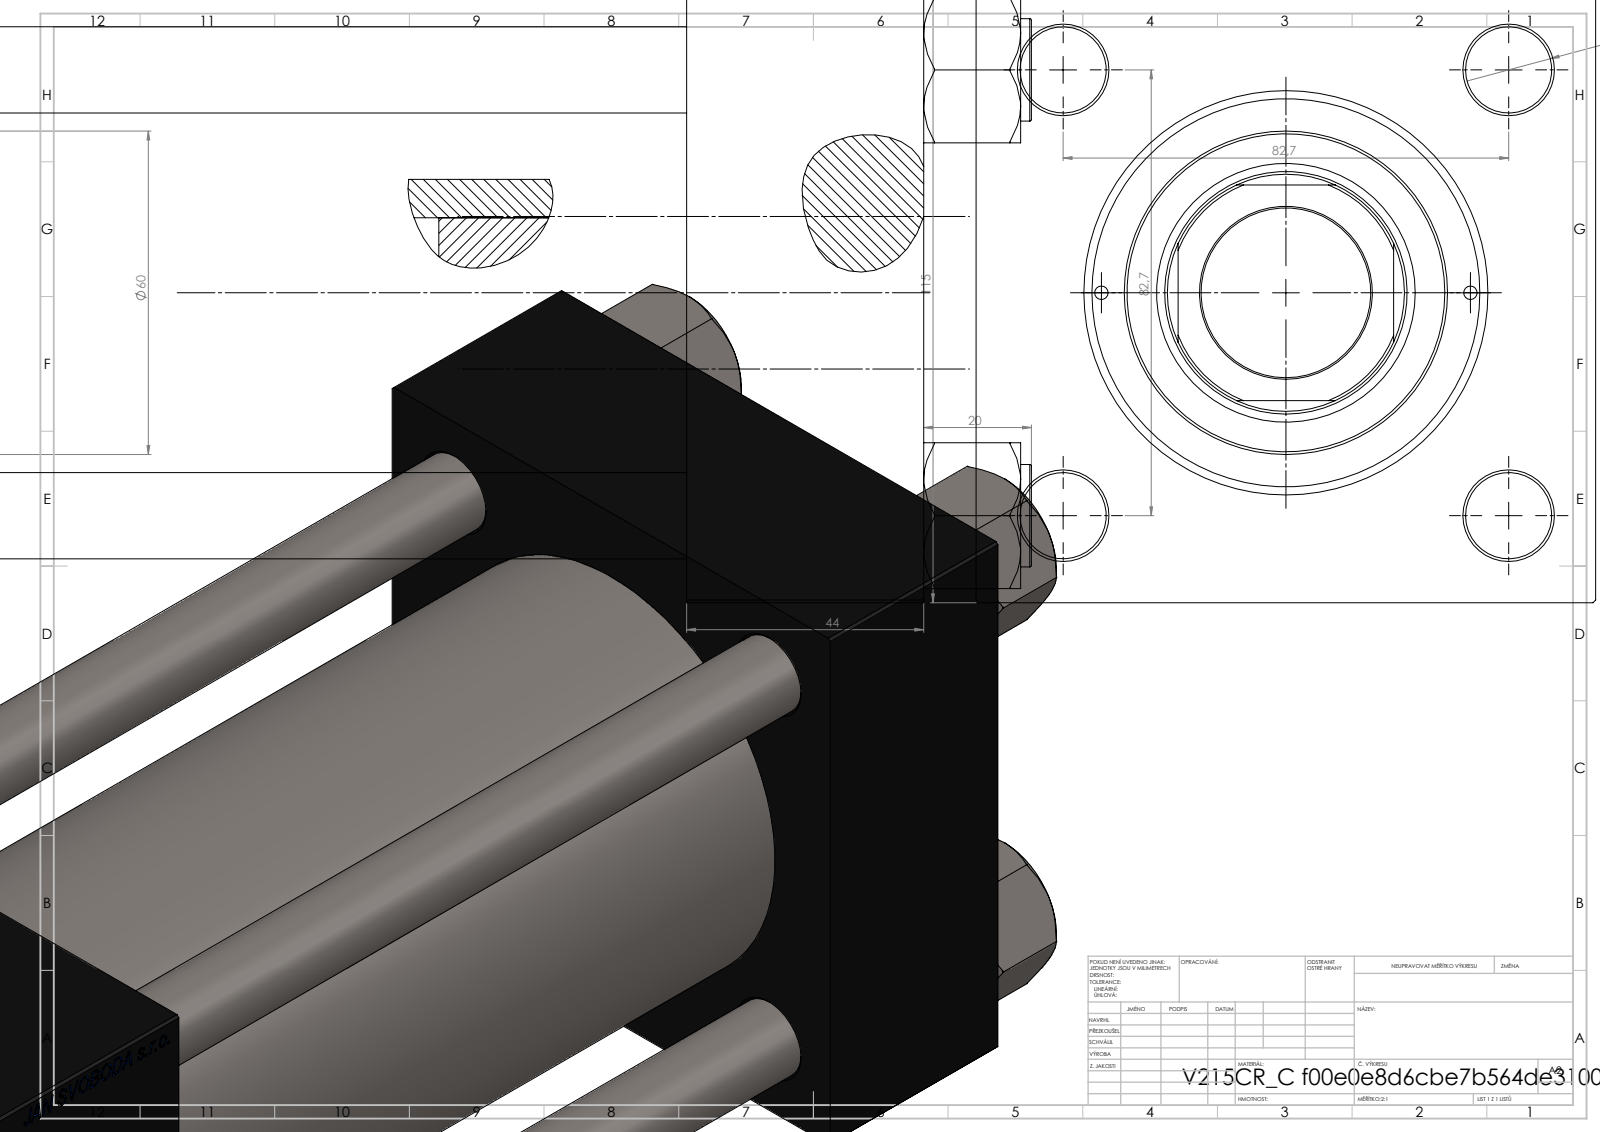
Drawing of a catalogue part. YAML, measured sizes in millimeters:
part_name: "V215_VC_A; V215CR_VCP_C; NUT_M5_C; V215CR_C_Body (+1 more)"
step_written_by: "SolidWorks 2019 (CONFIG_CONTROL_DESIGN)"
units: millimeters
bodies: {solids: 11, faces: 1202, planar: 576, cylindrical: 90, other: 536}
overall_size: [335, 115, 115]
volume: 2153000
surface_area: 364668
round_holes:
  - {diameter: 16, count: 4}
  - {diameter: 2.5, count: 2}
  - {diameter: 7, count: 2}
  - {diameter: 26.44, count: 2}
  - {diameter: 35, count: 2}
  - {diameter: 31.5, count: 1}
  - {diameter: 45, count: 1}
  - {diameter: 48, count: 1}
  - {diameter: 61, count: 1}
  - {diameter: 72, count: 1}
  - {diameter: 80, count: 1}
round_bosses_or_shafts:
  - {diameter: 19, count: 4}
  - {diameter: 86, count: 1}
  - {diameter: 60, count: 1}
partial_cylinders:
  - {radius: 22, count: 1}
face_to_face_distances: [115, 44, 284, 240, 215, 171, 69, 255.3, 211.3, 40.3]
hole_center_spacings: [41.96, 58.48, 82.7, 86.17, 34.25, 116.96, 68.5, 216]
